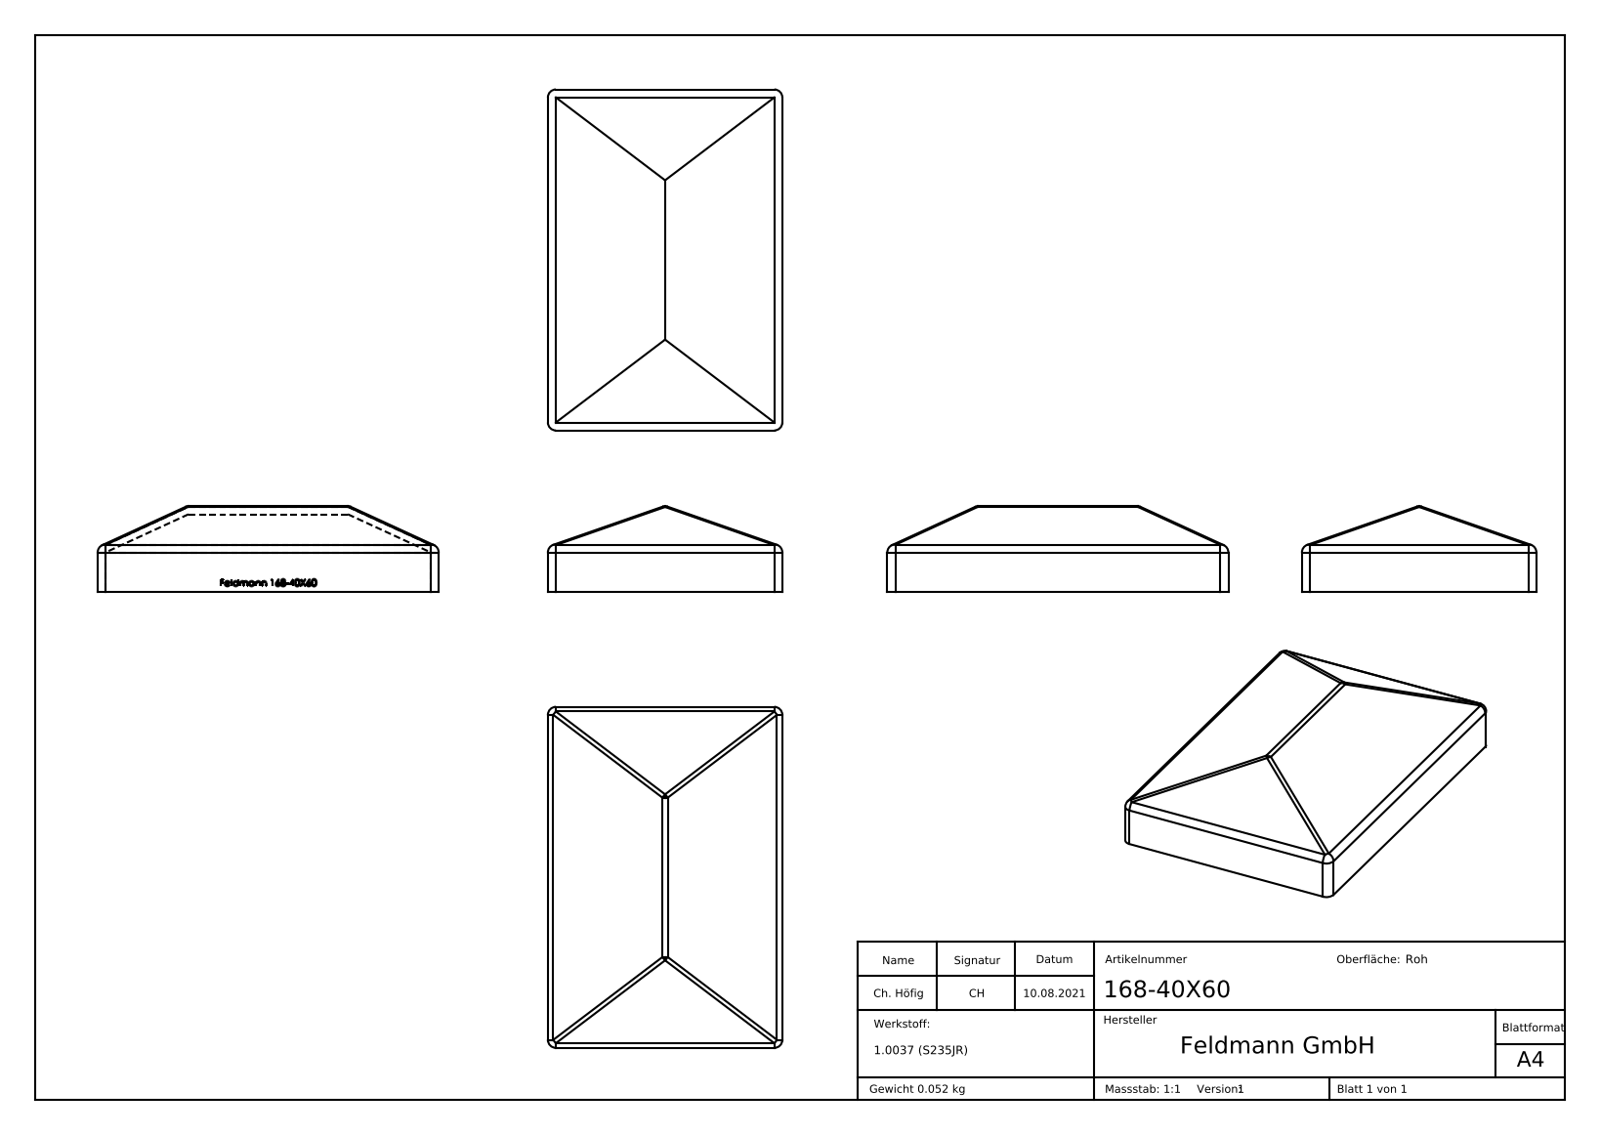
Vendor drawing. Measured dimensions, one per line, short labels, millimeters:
name: 168-40X60
written by: SolidWorks 2018 (CONFIG_CONTROL_DESIGN)
unit: mm
bodies: 1 solid, 263 faces (130 planar, 13 cylindrical, 120 other)
size: 64 × 44 × 16
volume: 6 683 mm³; area: 9 238 mm²
rounds: 13× R1.5
face distances: 1.5, 42.5, 62.5, 44, 41, 64, 61, 1.4, 41.1, 42.6
